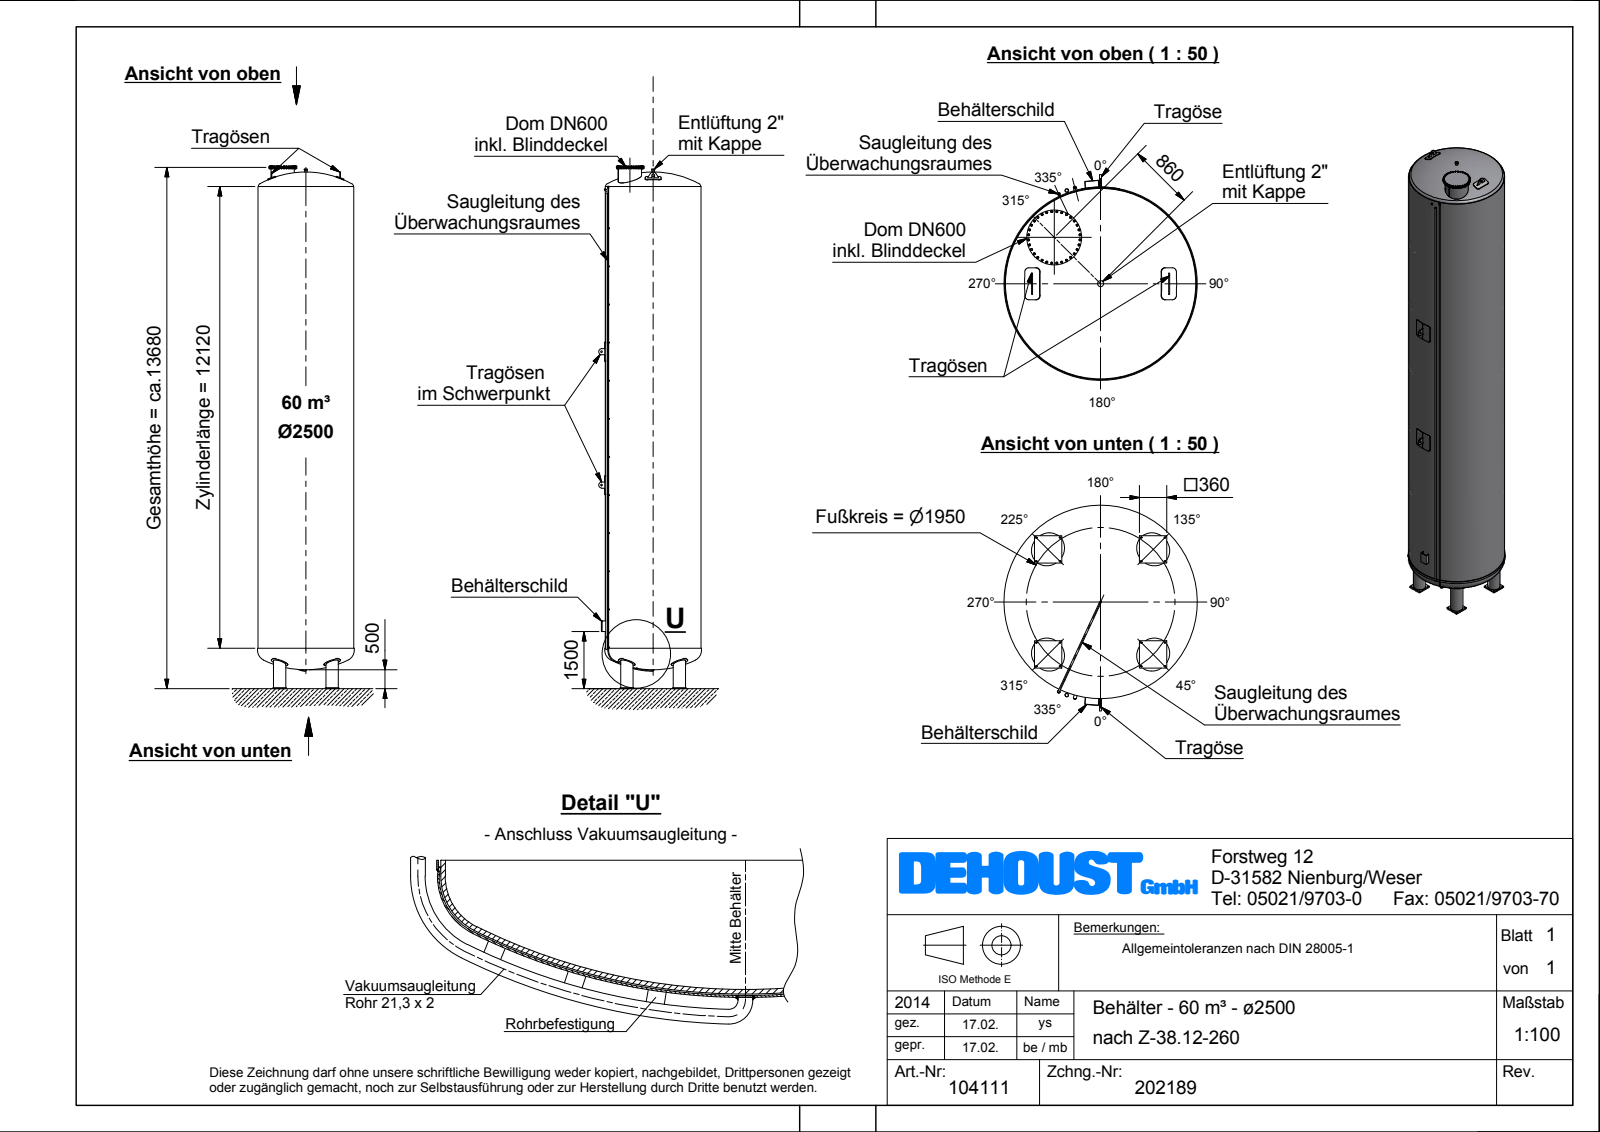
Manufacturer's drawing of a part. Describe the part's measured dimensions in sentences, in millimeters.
The part is named "Z-38_12-260_Beh\\S\\dlter_\\S\\x2500_060m\\S\\3_Dichte=1,0". Its 3-D file was written by "Autodesk Inventor 2012 (AUTOMOTIVE_DESIGN)". It is 20 solids with 1263 faces: 765 planar, 164 cylindrical and 334 other. Overall it measures 13708.78 by 2700 by 2540 millimeters. Its volume is 62 360 000 000 cubic millimeters and its surface area 131 700 000 square millimeters. Round holes: 4 of diameter 200, 4 of diameter 306.9, 1 of diameter 598. Round bosses or shafts: 32 of diameter 22.5, 32 of diameter 16, 4 of diameter 450, 4 of diameter 323.9, 2 of diameter 21.3, 1 of diameter 2540, 1 of diameter 2516, 1 of diameter 720. Partial cylindrical surfaces (rounded edges, fillets, slot ends): 8 of radius 50, 8 of radius 56, 2 of radius 80, 1 of radius 35, 1 of radius 85, 1 of radius 1259, 1 of radius 1269. The main face-to-face distances are 13181.09, 30, 13151.09, 13698.78, 13668.78, 517.69, 13663.78, 13633.78, 482.69, 35. The hole center spacings are 1378.86, 1300.09, 1950, 115, 1835.
